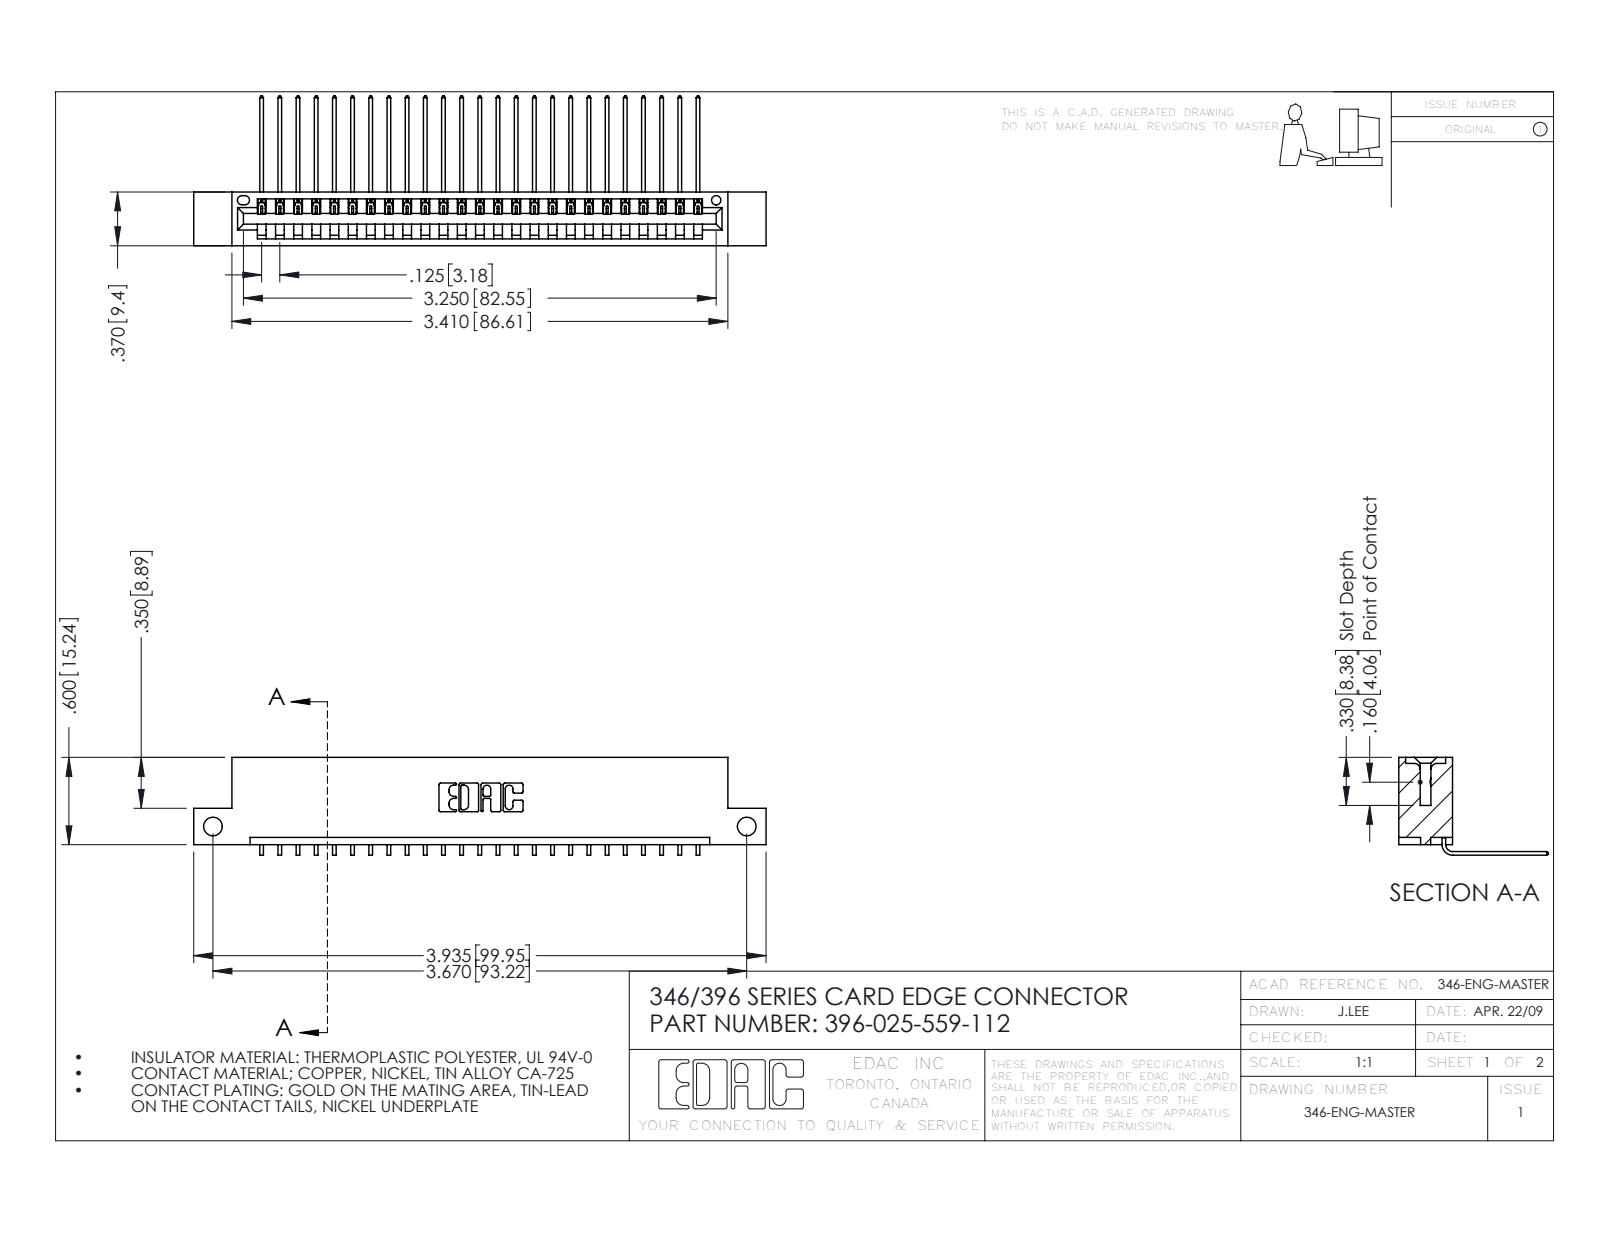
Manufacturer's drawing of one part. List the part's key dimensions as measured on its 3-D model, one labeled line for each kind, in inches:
Part name (STEP PRODUCT): 396-025-559-112; 345-292-001_558 559 Tail - 1; 346 Part_Flush Mounting Lugs - Side Mount
STEP written by: SolidWorks 2016 (CONFIG_CONTROL_DESIGN)
Units: inches
Bodies: 26 solids, 1622 faces (1126 planar, 496 cylindrical, 0 other)
Overall size (bounding box): 3.935 × 1.03 × 0.673
Volume: 0.576 in³ · Surface area: 18.56 in²
Round holes (diameter × count): ⌀0.128 ×2, ⌀0.064 ×1
Partial cylindrical surfaces — rounded edges, fillets, slot ends (radius × count): R0.006 ×50, R0.01 ×22, R0.007 ×6, R0.031 ×6, R0.026 ×3, R0.031 ×2, R0.04 ×2, R0.014 ×1
Main face-to-face distances: 0.048, 0.322, 0.37, 0.25, 0.072, 0.025, 0.298, 0.148, 0.222, 0.1
Hole centre spacings: 3.67
